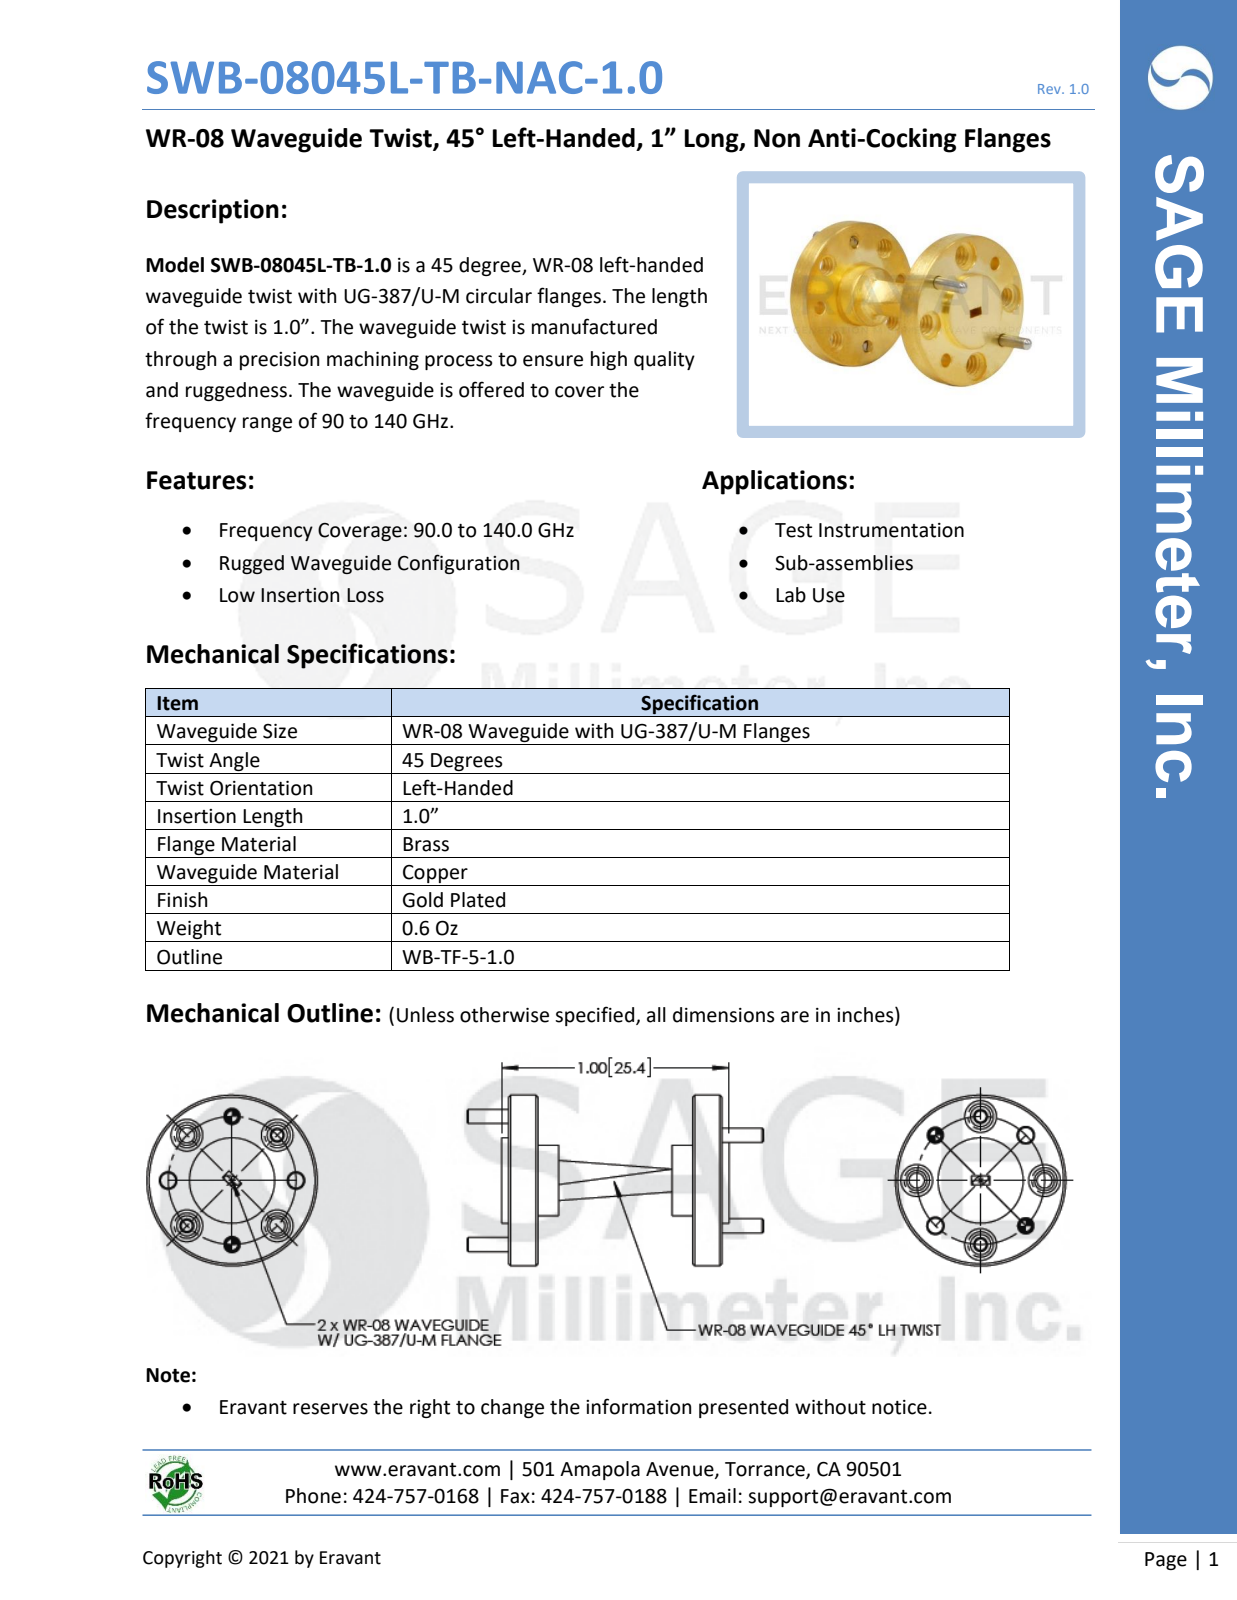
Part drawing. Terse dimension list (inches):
name: SWB-08045L-TB-1.0
written by: SolidWorks 2016 (AUTOMOTIVE_DESIGN)
unit: in
bodies: 5 solids, 146 faces (34 planar, 68 cylindrical, 44 other)
size: 1.305 × 0.75 × 0.75
volume: 0.134 in³; area: 3.413 in²
holes: 8× ⌀0.089, 8× ⌀0.14, 4× ⌀0.061, 4× ⌀0.067
bosses: 4× ⌀0.063, 1× ⌀0.75, 1× ⌀0.375, 1× ⌀0.31
face distances: 0.13, 0.81, 0.68, 0.94, 0.03, 0.16, 0.84, 0.97, 0.25, 0.75
hole spacings: 0.215, 0.398, 0.519, 0.562
